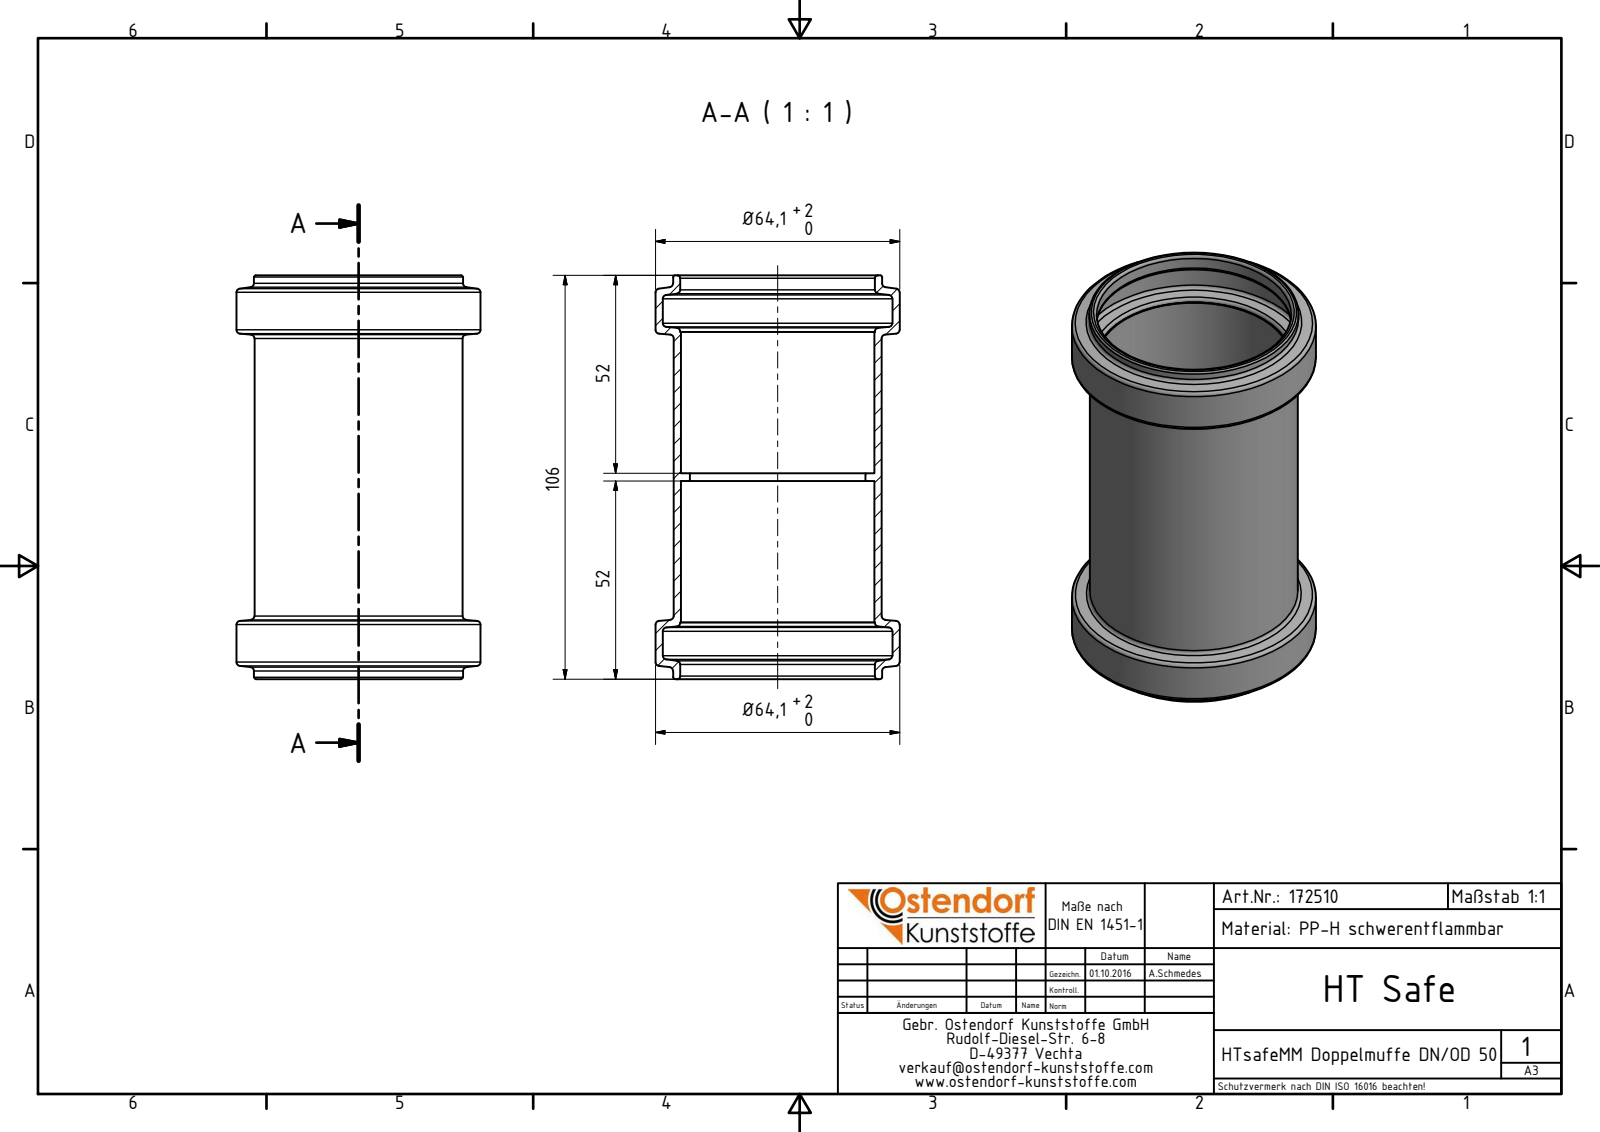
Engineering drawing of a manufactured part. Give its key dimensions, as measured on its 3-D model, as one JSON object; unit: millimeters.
{"part_name": "172510 HTsafeMM DN_OD 50", "step_written_by": "Autodesk Inventor 2016 (AUTOMOTIVE_DESIGN)", "units": "millimeters", "bodies": {"solids": 1, "faces": 48, "planar": 6, "cylindrical": 14, "other": 28}, "overall_size": [106, 64.1, 64.1], "volume_mm3": 40929, "surface_area_mm2": 42618, "round_holes": [[46.1, 1], [50.8, 1], [51.1, 1], [60.3, 1]], "round_bosses_or_shafts": [[64.1, 1], [54.9, 1], [54.6, 1]], "face_to_face_distances": [2, 52, 54, 106, 14.9, 91.1, 37.1, 39.1, 76.2]}
